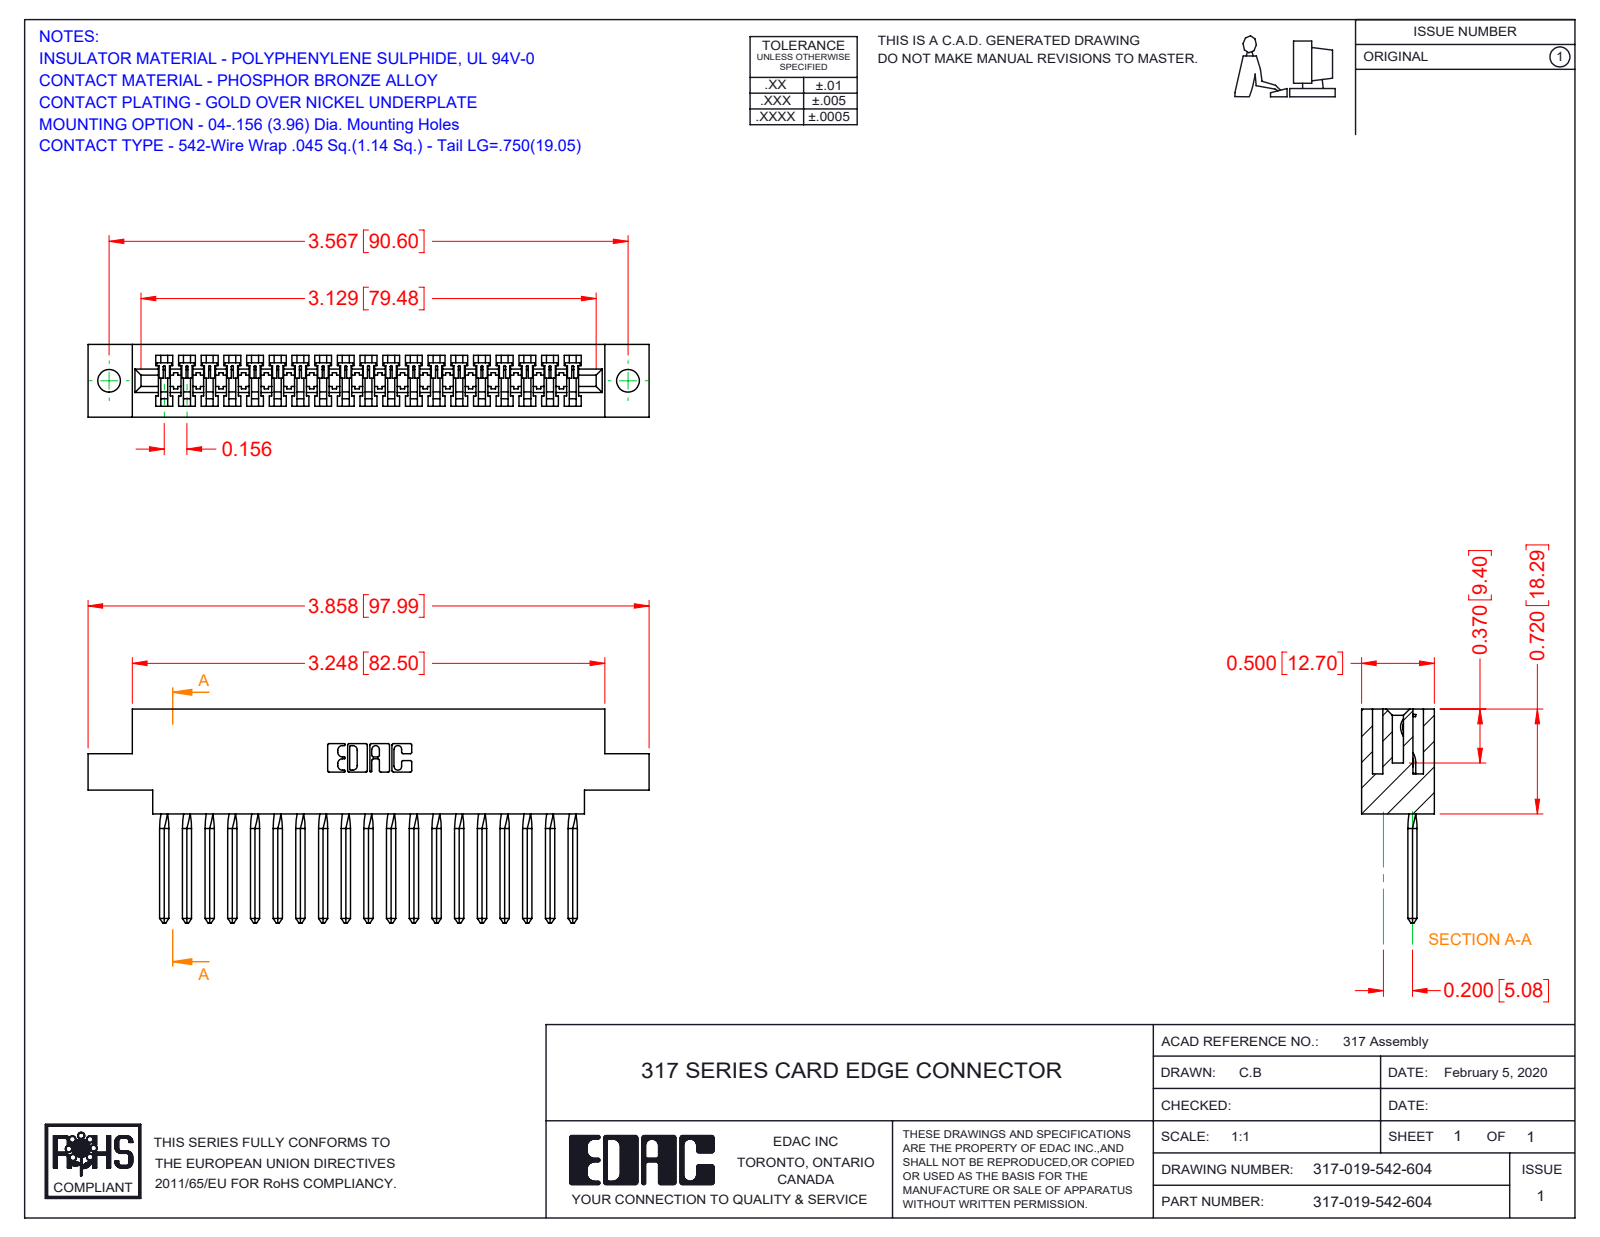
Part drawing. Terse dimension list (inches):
name: 317-290-003_542; 317 Part_.156 Dia - TH; 317-019-542-604
written by: SolidWorks 2016 (CONFIG_CONTROL_DESIGN)
unit: in
bodies: 20 solids, 1527 faces (1274 planar, 177 cylindrical, 76 other)
size: 3.858 × 1.47 × 0.5
volume: 0.881 in³; area: 26.2 in²
holes: 2× ⌀0.156
rounds: 38× R0.006, 22× R0.01, 6× R0.007, 6× R0.031, 3× R0.026, 1× R0.074, 1× R0.089, 1× R0.1
face distances: 0.5, 0.075, 0.425, 0.35, 0.11, 0.136, 0.72, 0.279, 0.211, 0.289
hole spacings: 3.567
